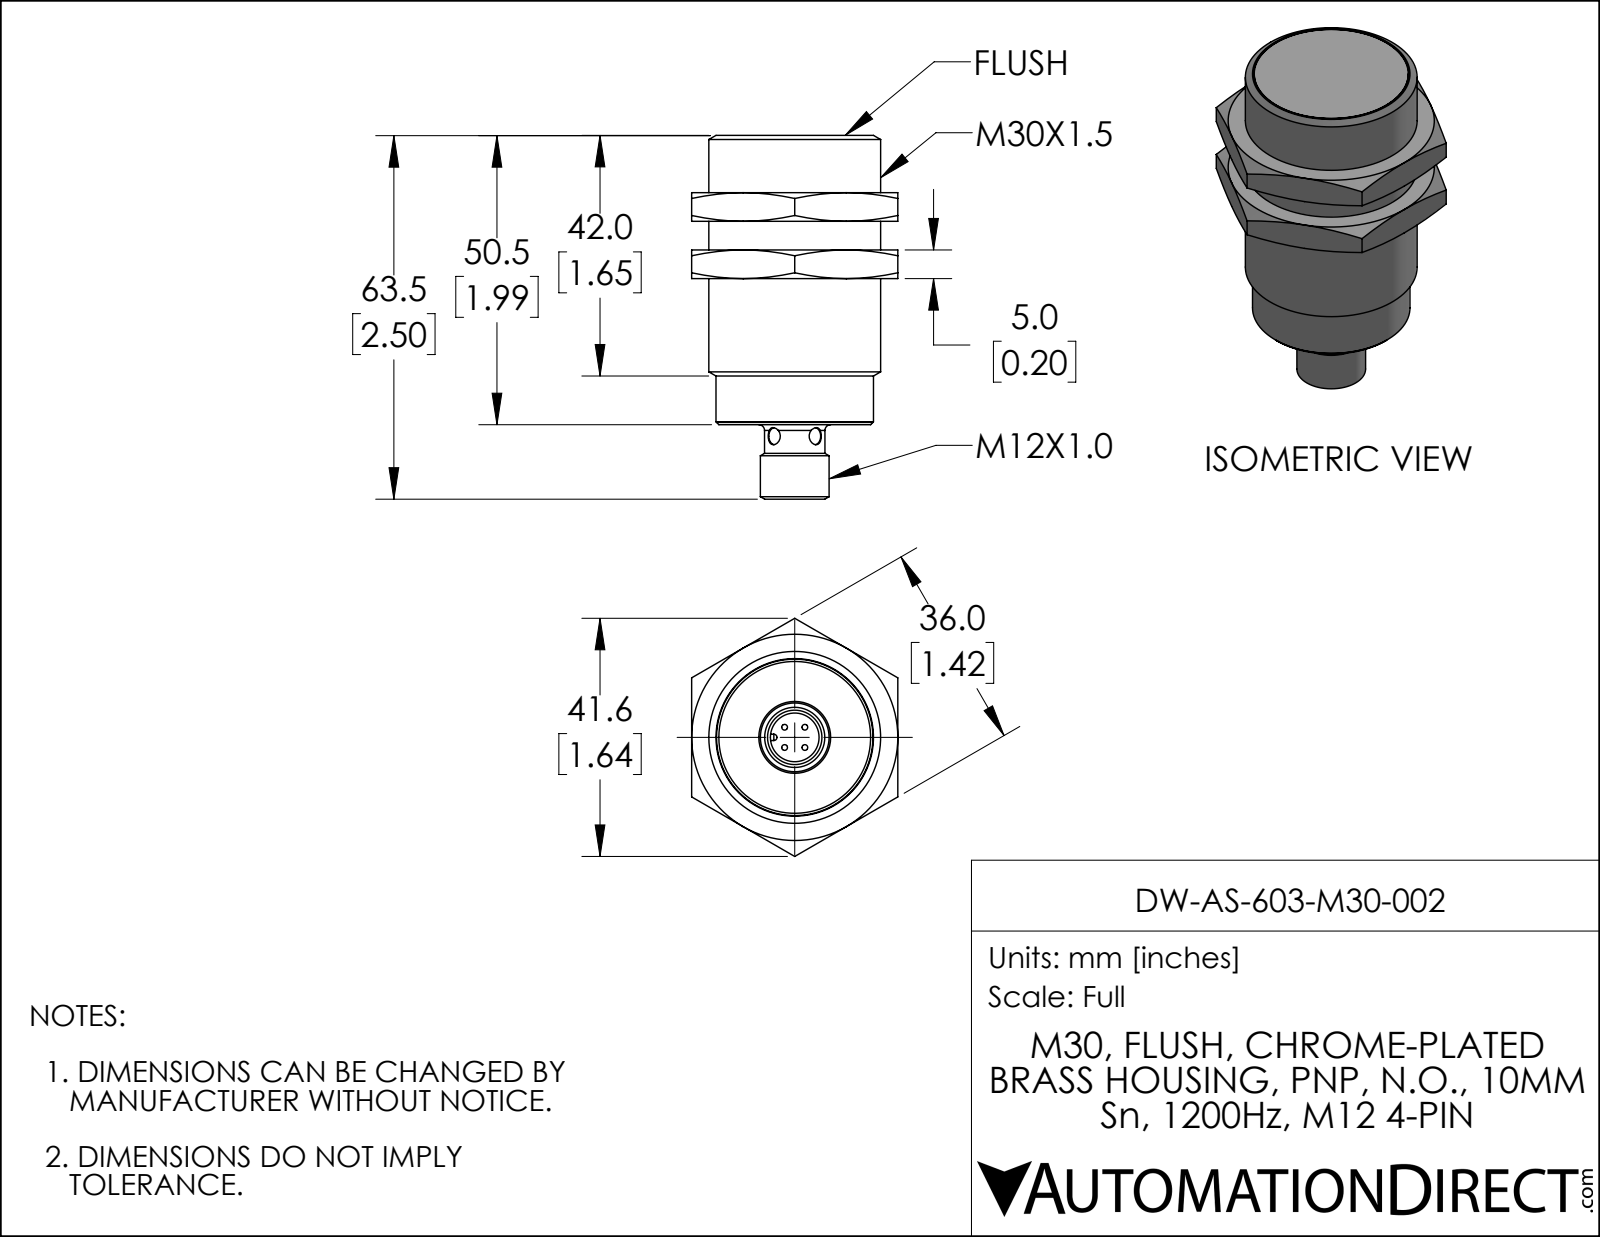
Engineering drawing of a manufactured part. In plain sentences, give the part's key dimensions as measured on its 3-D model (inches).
The part is named "DW-AS-603-M30-002". Its 3-D file was written by "SolidWorks 2019 (AUTOMOTIVE_DESIGN)". It is 1 solid with 85 faces: 29 planar, 20 cylindrical and 36 other. Overall it measures 2.5 by 1.637 by 1.417 inches. Its volume is 2.412 cubic inches and its surface area 13.37 square inches. Round holes: 2 of diameter 0.118, 1 of diameter 0.335, 1 of diameter 1.068. Round bosses or shafts: 4 of diameter 0.039, 1 of diameter 1.181, 1 of diameter 1.083, 1 of diameter 1.075, 1 of diameter 1.059, 1 of diameter 0.472, 1 of diameter 0.415. Partial cylindrical surfaces (rounded edges, fillets, slot ends): 2 of radius 0.022. The main face-to-face distances are 0.394, 0.197, 0.591, 1.417, 1.988, 0.984, 0.787, 1.594, 1.201, 1.004.
